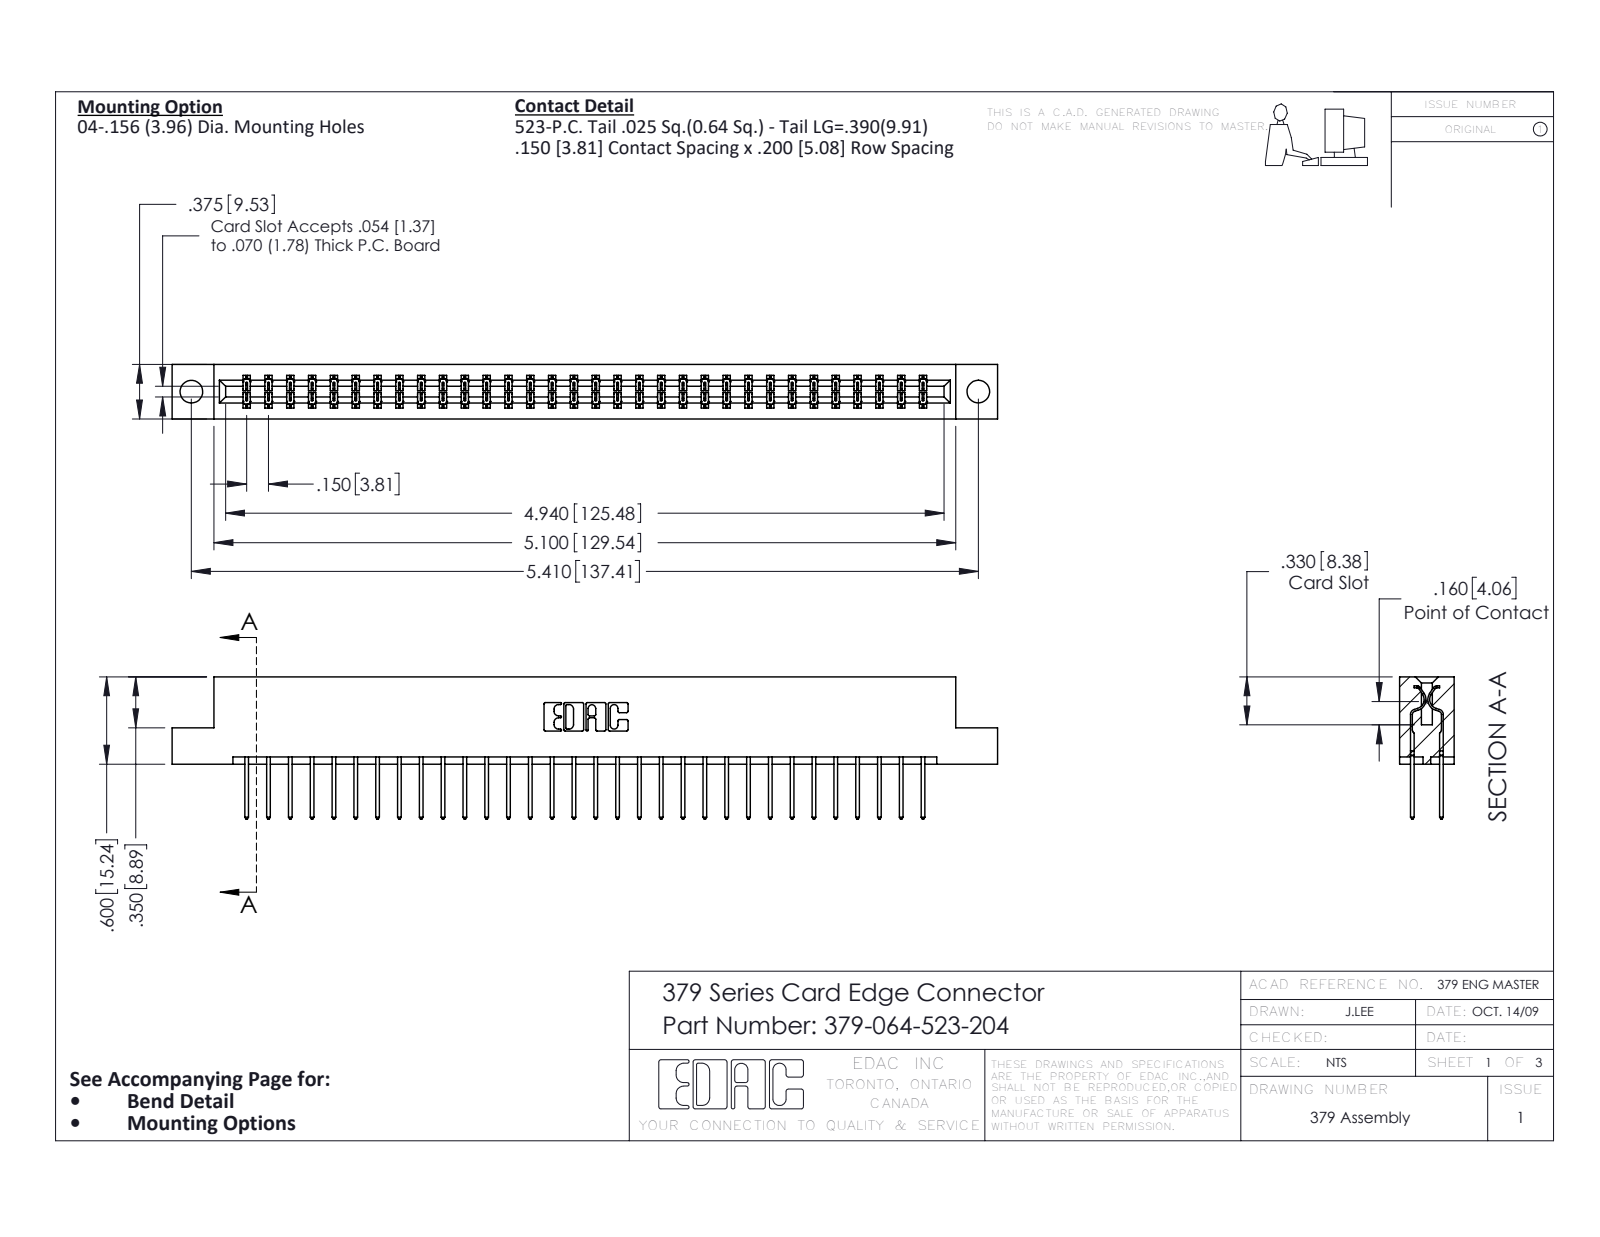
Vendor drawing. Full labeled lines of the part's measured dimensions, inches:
Part name (STEP PRODUCT): 379 Part_Flush - .156 Dia - TH; 345-292-001_345-293-123; 379-064-523-204
STEP written by: SolidWorks 2016 (CONFIG_CONTROL_DESIGN)
Units: inches
Bodies: 65 solids, 3442 faces (2374 planar, 1068 cylindrical, 0 other)
Overall size (bounding box): 5.675 × 0.977 × 0.375
Volume: 0.932 in³ · Surface area: 27.11 in²
Round holes (diameter × count): ⌀0.156 ×2
Partial cylindrical surfaces — rounded edges, fillets, slot ends (radius × count): R0.006 ×96, R0.01 ×64, R0.01 ×22, R0.007 ×6, R0.031 ×6, R0.026 ×3, R0.014 ×2, R0.022 ×2
Main face-to-face distances: 0.3, 0.075, 0.375, 0.2, 0.1, 0.275, 0.225, 0.025, 0.15, 0.076
Hole centre spacings: 5.41
